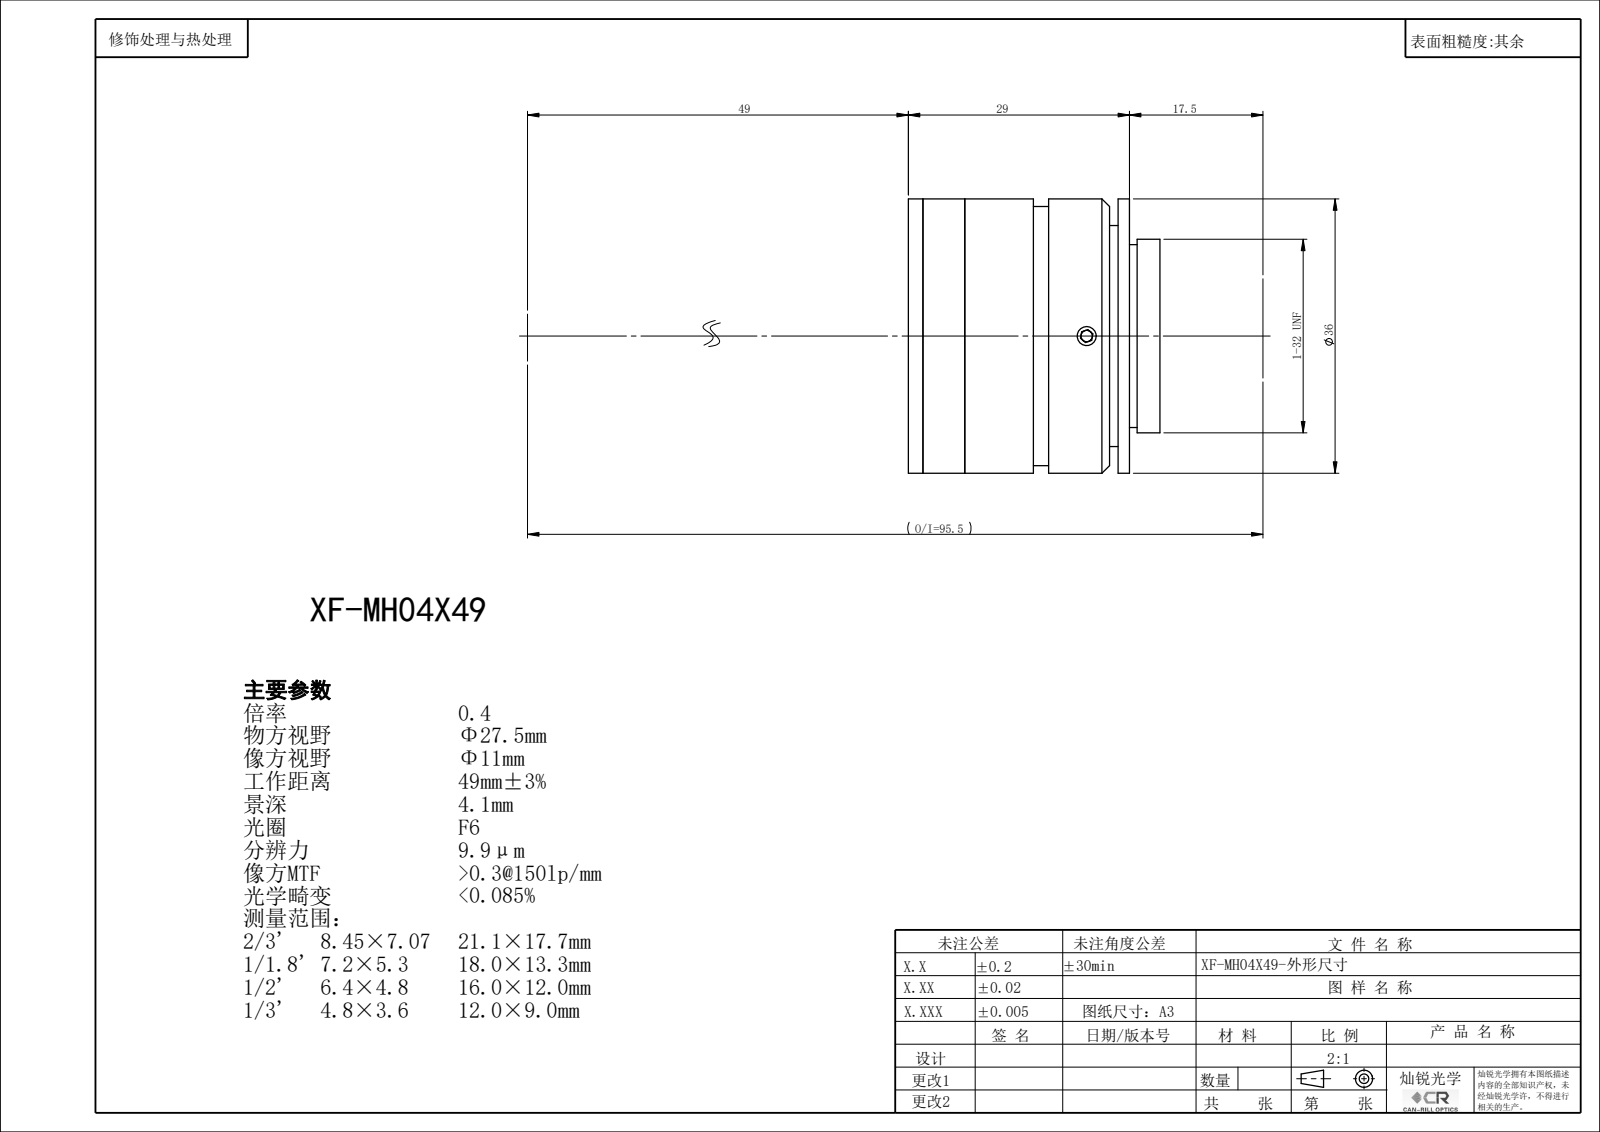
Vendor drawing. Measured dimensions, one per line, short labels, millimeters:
name: XF-MH04X49
written by: SolidWorks 2022 (CONFIG_CONTROL_DESIGN)
unit: mm
bodies: 0 solids, 114 faces (54 planar, 50 cylindrical, 10 other)
size: 36 × 36 × 33.03
holes: 3× ⌀2.5, 1× ⌀7, 1× ⌀8.4, 1× ⌀10, 1× ⌀12, 1× ⌀14, 1× ⌀16, 1× ⌀18, 1× ⌀20, 1× ⌀21.5, 1× ⌀22, 1× ⌀24
bosses: 1× ⌀36, 1× ⌀34, 1× ⌀25.4, 1× ⌀9
face distances: 5.5, 7.41, 27.12, 21.62, 1.91, 29.03, 25.62, 2, 1, 1.5
